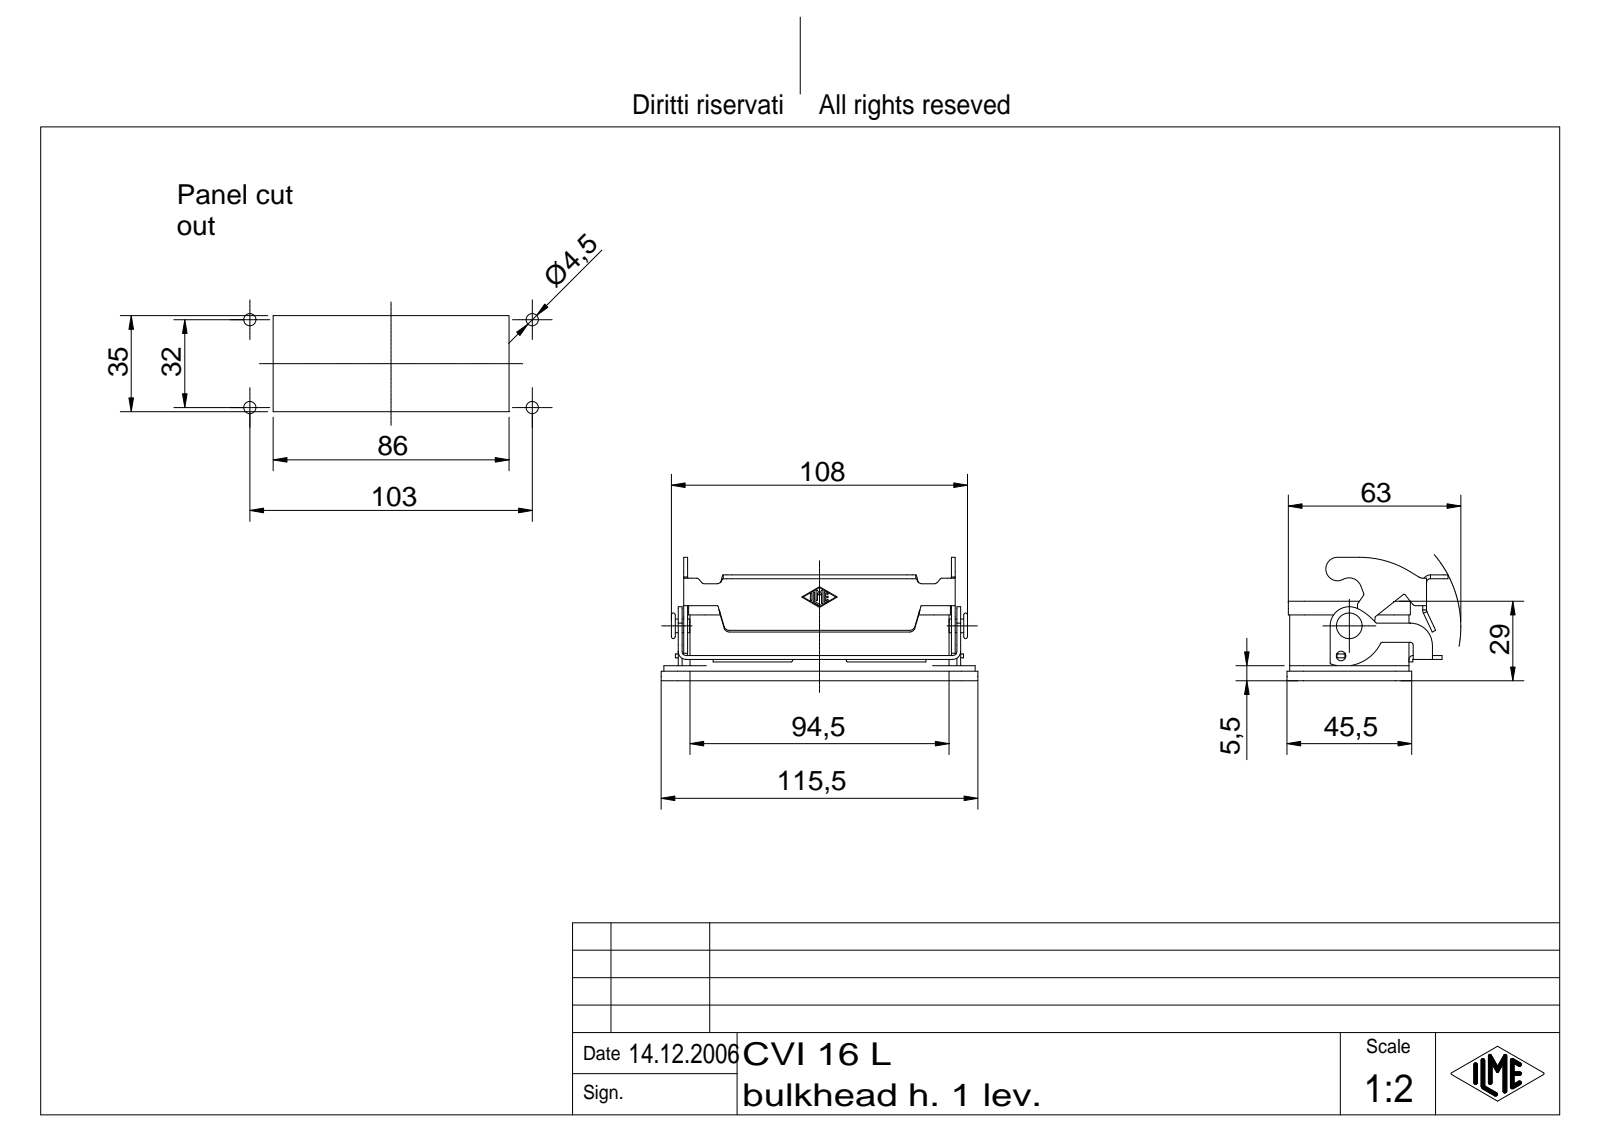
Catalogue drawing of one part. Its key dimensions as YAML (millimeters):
part_name: "CVI 16 L"
step_written_by: "Autodesk Inventor 7 (AUTOMOTIVE_DESIGN)"
units: millimeters
bodies: {solids: 2, faces: 419, planar: 141, cylindrical: 136, other: 142}
overall_size: [115.5, 58.73, 45]
volume: 39837
surface_area: 33608
round_holes:
  - {diameter: 4.5, count: 4}
  - {diameter: 4.5, count: 4}
  - {diameter: 3.5, count: 1}
round_bosses_or_shafts:
  - {diameter: 5, count: 1}
  - {diameter: 3.2, count: 1}
  - {diameter: 3, count: 1}
partial_cylinders:
  - {radius: 0.25, count: 15}
  - {radius: 3, count: 12}
  - {radius: 6, count: 12}
  - {radius: 0.5, count: 9}
  - {radius: 1.5, count: 9}
  - {radius: 1, count: 8}
  - {radius: 1.4, count: 6}
  - {radius: 2, count: 6}
face_to_face_distances: [40.5, 0.5, 3, 3.5, 4, 1.4, 43.5, 1, 37.5, 41]
hole_center_spacings: [32, 103, 107.86]
